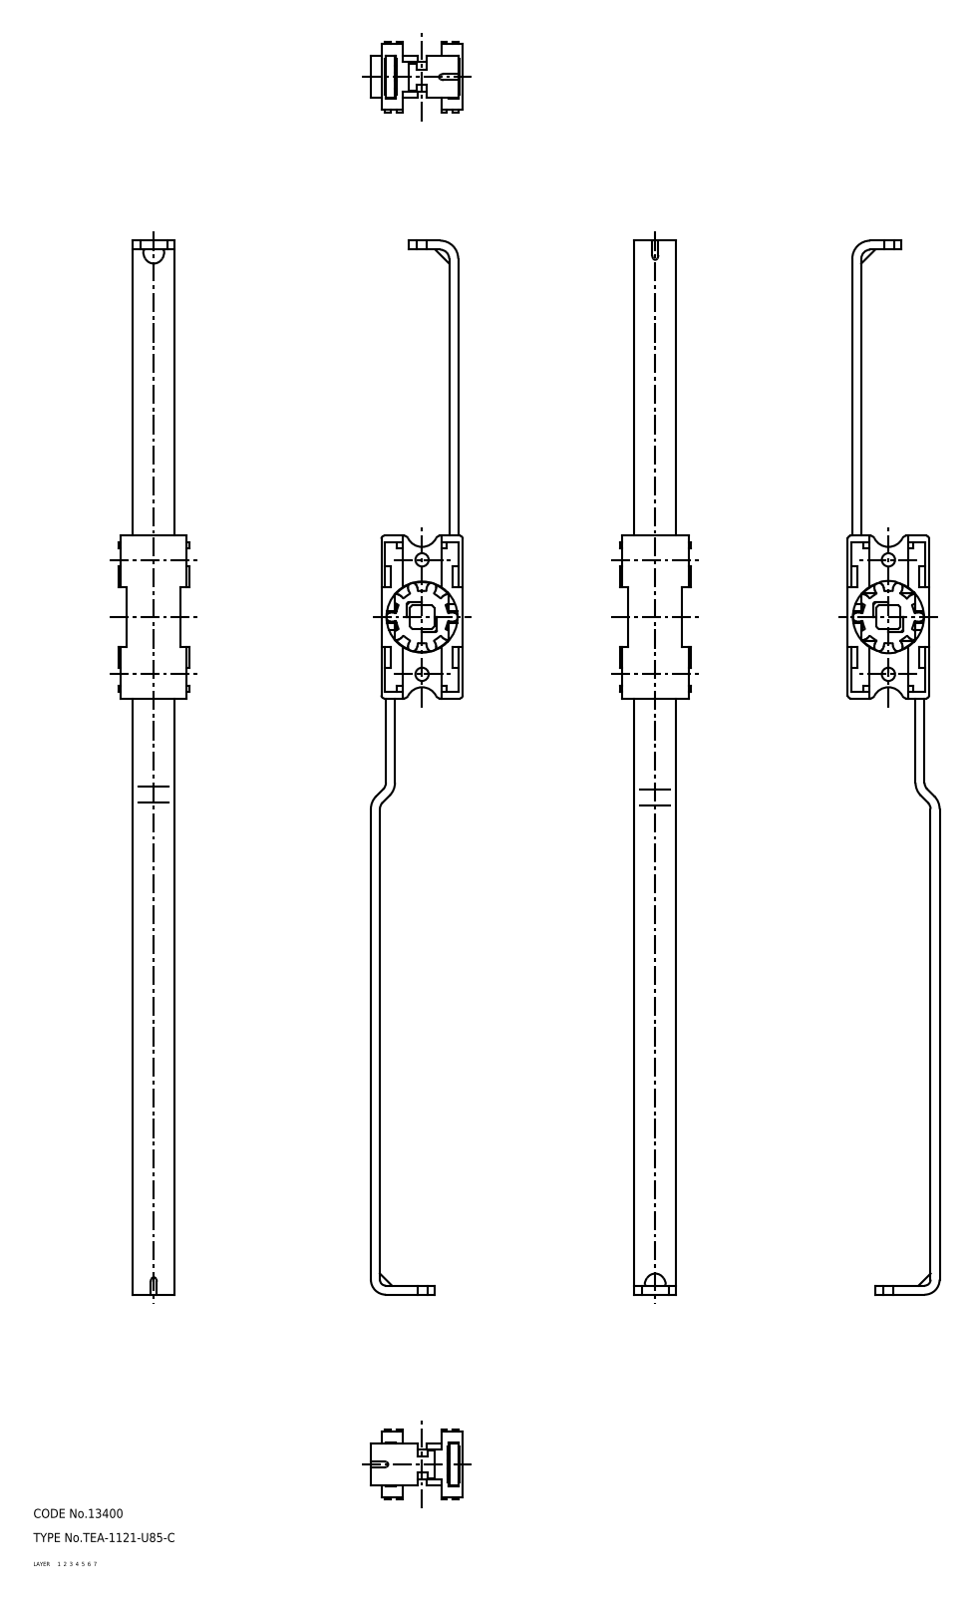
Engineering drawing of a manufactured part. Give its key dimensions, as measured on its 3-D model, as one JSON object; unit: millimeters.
{"part_name": "rod_2; rod_1; TEA_1121_U85_C_8271_36", "step_written_by": "CADfix (AUTOMOTIVE_DESIGN)", "units": "millimeters", "bodies": {"solids": 3, "faces": 612, "planar": 0, "cylindrical": 0, "other": 612}, "overall_size": [350, 30.5, 23.4], "volume_mm3": 29154, "surface_area_mm2": 25629}
